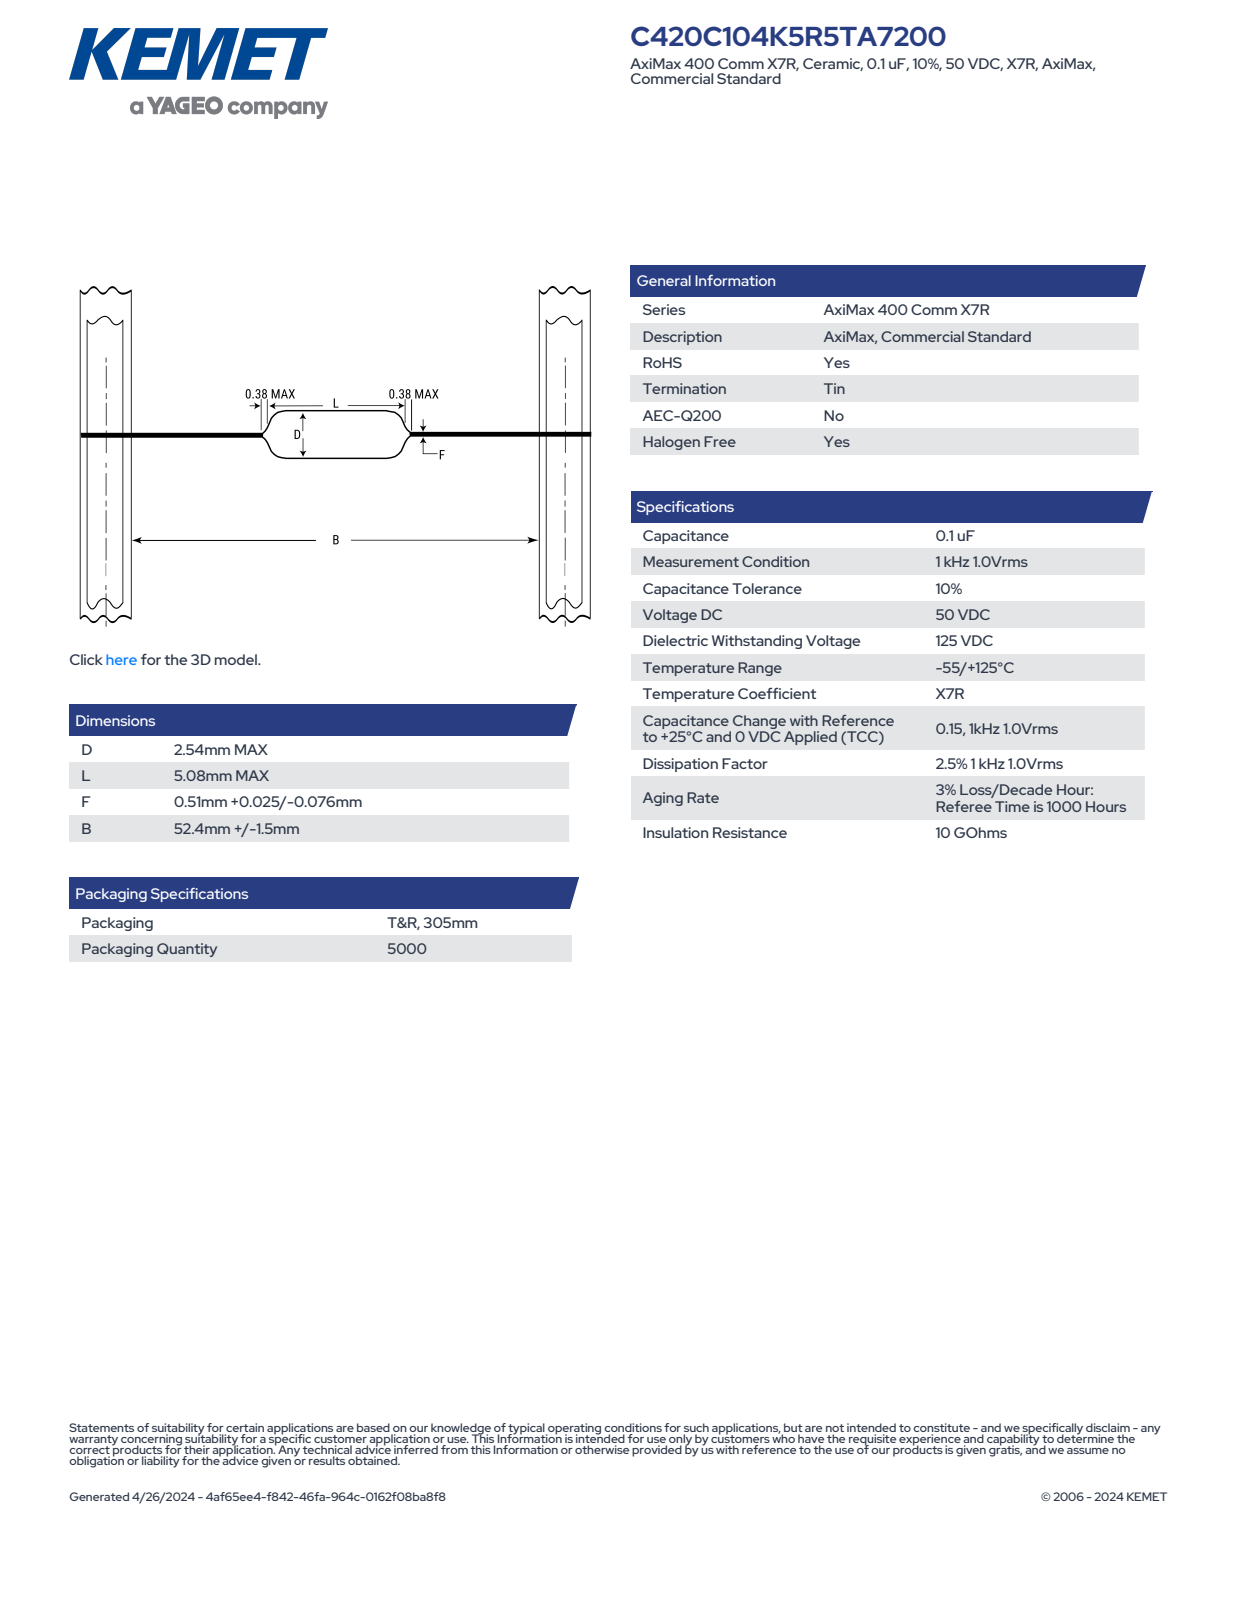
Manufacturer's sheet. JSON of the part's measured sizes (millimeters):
{"part_name": "CCA_ACSTTAPE_C420_D2.54L5.08LL25.4F0.535", "step_written_by": "SolidWorks 2014 (AUTOMOTIVE_DESIGN)", "units": "millimeters", "bodies": {"solids": 1, "faces": 74, "planar": 26, "cylindrical": 9, "other": 39}, "overall_size": [56.64, 2.54, 2.54], "volume_mm3": 37, "surface_area_mm2": 133, "round_bosses_or_shafts": [[2.54, 1], [0.54, 1]], "partial_cylinders_radius": [[1.26, 1]], "face_to_face_distances": [5.08, 25.78, 30.86, 56.64]}
